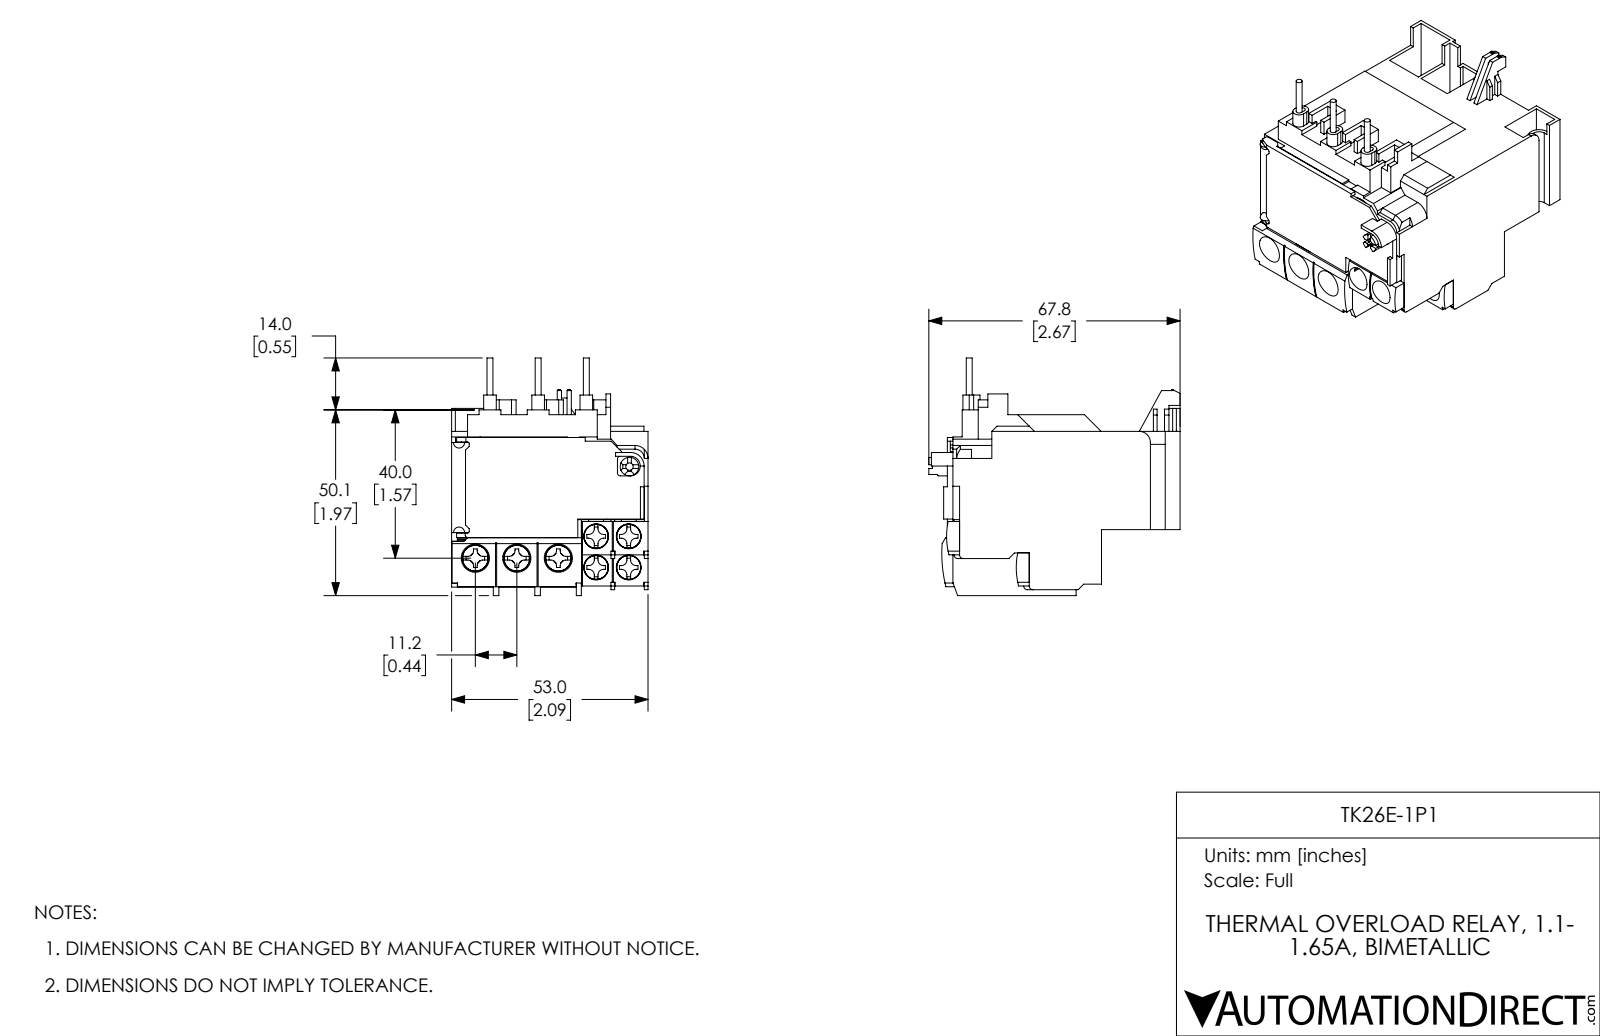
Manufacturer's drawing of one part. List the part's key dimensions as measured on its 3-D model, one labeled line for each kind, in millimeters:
Part name (STEP PRODUCT): TK26E-1P1
STEP written by: SolidWorks 2017 (AUTOMOTIVE_DESIGN)
Units: millimetres
Bodies: 38 solids, 1480 faces (1225 planar, 220 cylindrical, 35 other)
Overall size (bounding box): 67.8 × 64.1 × 53
Volume: 99 940 mm³ · Surface area: 38 810 mm²
Round holes (diameter × count): ⌀3.5 ×4, ⌀3.6 ×4, ⌀6.7 ×4, ⌀4 ×3, ⌀4.1 ×3, ⌀7.6 ×3, ⌀1 ×1, ⌀2 ×1, ⌀5 ×1, ⌀11 ×1
Round bosses / shafts (diameter × count): ⌀6.6 ×4, ⌀1.6 ×3, ⌀6 ×1
Partial cylindrical surfaces — rounded edges, fillets, slot ends (radius × count): R1.5 ×28, R1 ×8, R0.5 ×6, R1.7 ×6, R0.8 ×5, R1.2 ×4, R4.3 ×4, R4.8 ×3
Main face-to-face distances: 1, 9, 1.5, 12, 53, 2, 10, 11, 8.7, 0.7
Hole centre spacings: 8.4, 8.8, 11.2, 12.2, 9.6, 10.5, 11.8, 18.8
